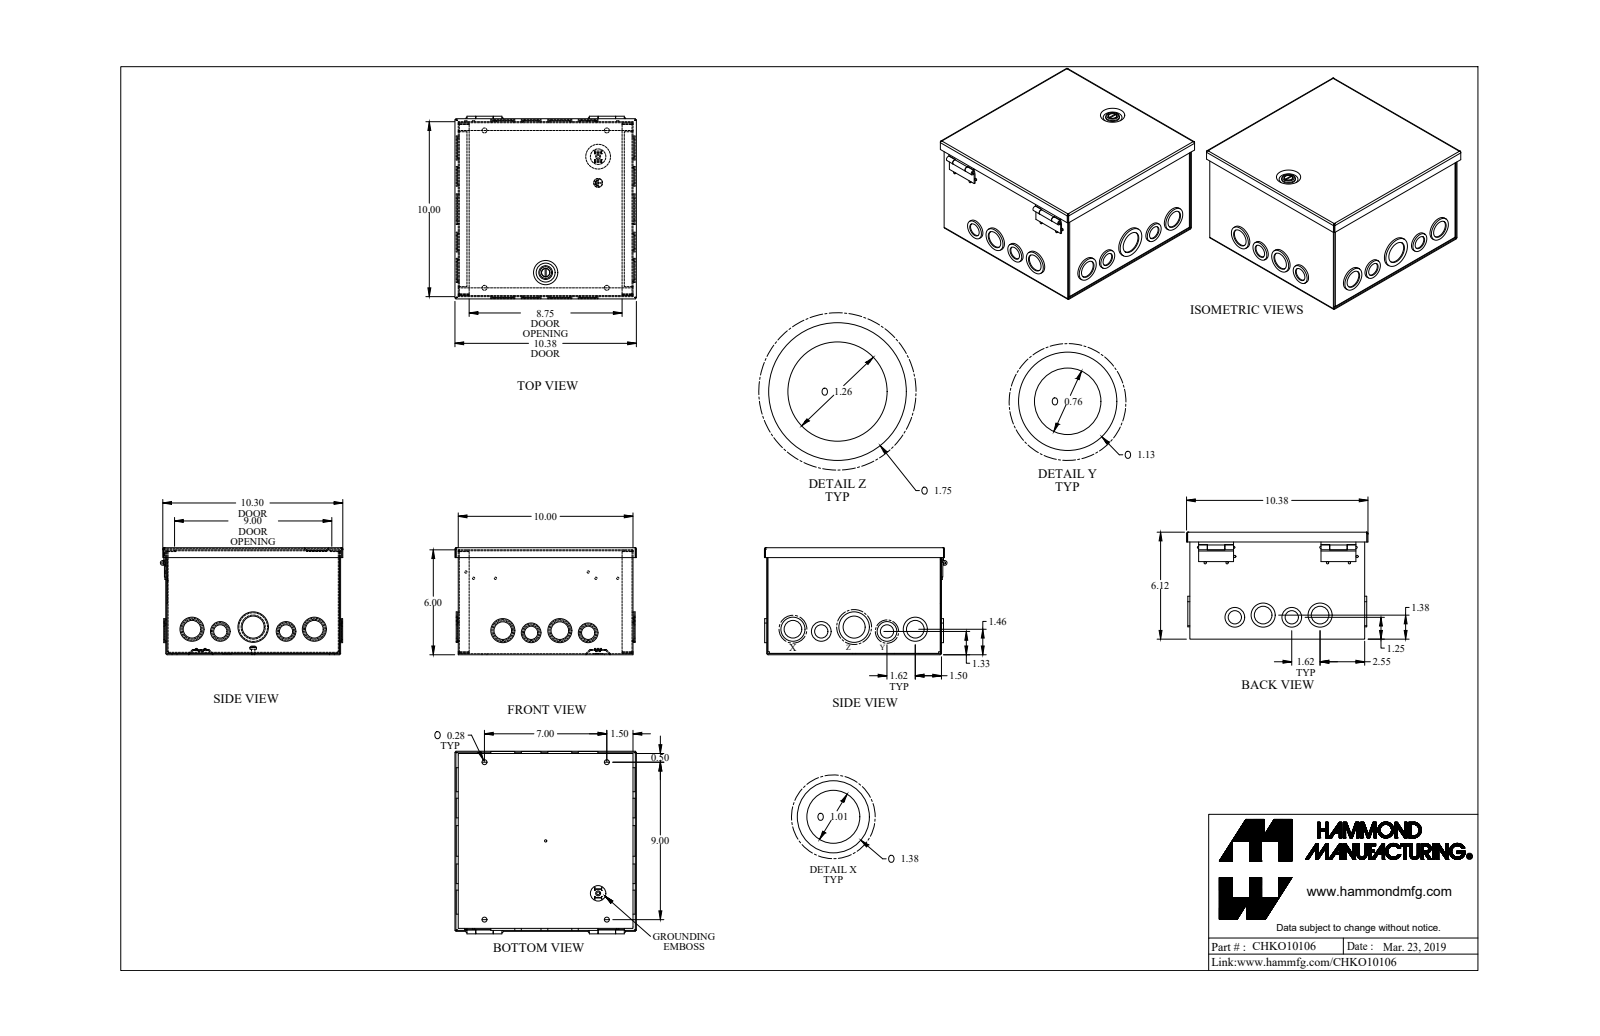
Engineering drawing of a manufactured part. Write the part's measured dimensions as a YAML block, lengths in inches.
part_name: "CHKO10106_Default"
step_written_by: "SolidWorks 2019 (CONFIG_CONTROL_DESIGN)"
units: inches
bodies: {solids: 12, faces: 703, planar: 344, cylindrical: 316, other: 43}
overall_size: [10.443, 10.38, 6.118]
volume: 30.15
surface_area: 1063
round_holes:
  - {diameter: 1.011, count: 8}
  - {diameter: 1.261, count: 6}
  - {diameter: 0.281, count: 4}
  - {diameter: 0.761, count: 4}
  - {diameter: 0.125, count: 1}
  - {diameter: 0.17, count: 1}
  - {diameter: 0.319, count: 1}
  - {diameter: 0.476, count: 1}
  - {diameter: 0.5, count: 1}
  - {diameter: 1.636, count: 1}
round_bosses_or_shafts:
  - {diameter: 0.131, count: 8}
  - {diameter: 1.125, count: 6}
  - {diameter: 1.375, count: 5}
  - {diameter: 0.875, count: 4}
  - {diameter: 1.375, count: 3}
  - {diameter: 1.125, count: 2}
  - {diameter: 0.875, count: 2}
  - {diameter: 1.75, count: 1}
partial_cylinders:
  - {radius: 0.029, count: 16}
  - {radius: 0.086, count: 16}
  - {radius: 0.057, count: 8}
  - {radius: 0.012, count: 4}
  - {radius: 0.1, count: 4}
  - {radius: 0.036, count: 2}
  - {radius: 0.079, count: 2}
  - {radius: 0.25, count: 2}
face_to_face_distances: [0.057, 9.943, 6.061, 10, 9.886, 6.118, 6.004, 5.943, 0.118, 0.07]
hole_center_spacings: [1.625, 3.26, 7, 1.896, 3.502, 4.881, 5.381, 9]
